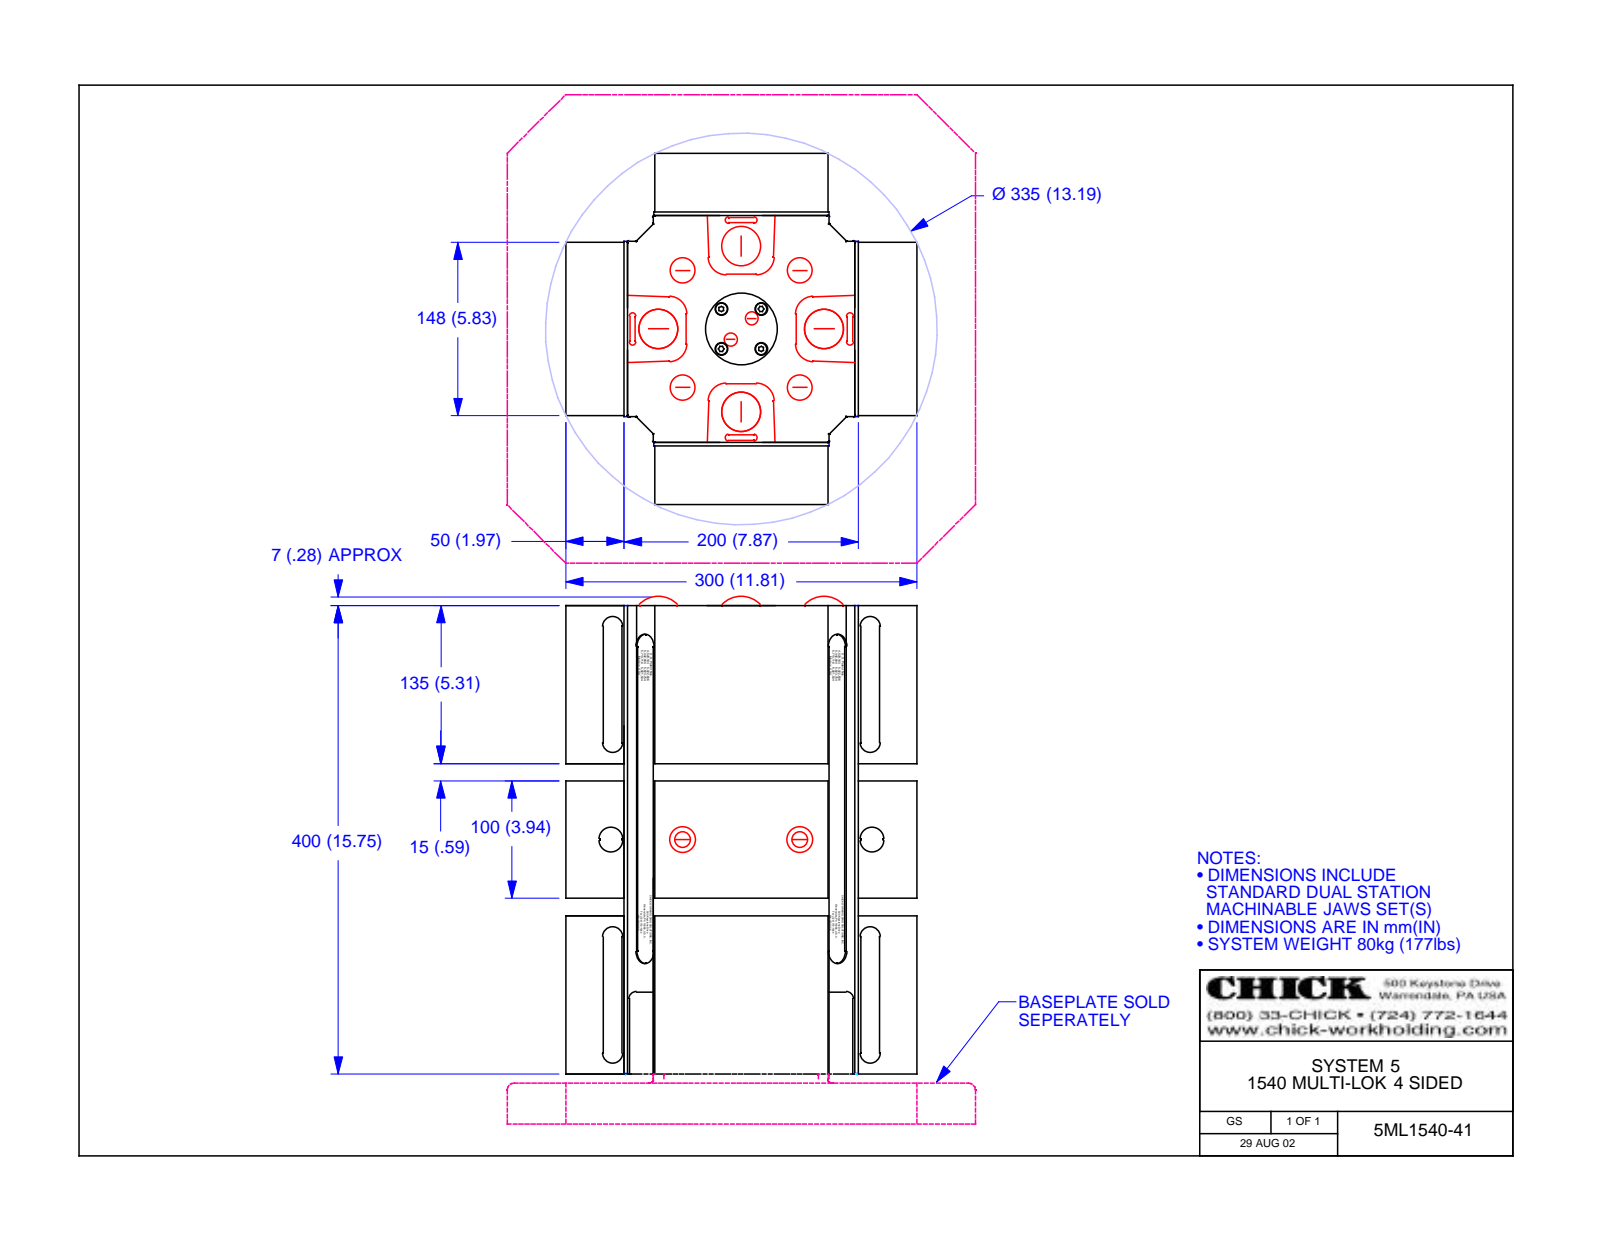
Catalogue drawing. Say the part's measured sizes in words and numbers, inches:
The part is named "5ML1540-41; 5CLM1540-41CM; 5CP1540-ST; 5DS1540-15-50 (+2 more)". Its 3-D file was written by "Autodesk Inventor 2013 (AUTOMOTIVE_DESIGN)". It is 17 solids with 2544 faces: 1308 planar, 456 cylindrical and 780 other. Overall it measures 16.031 by 11.811 by 11.811 inches. Its volume is 1 367 cubic inches and its surface area 2 866 square inches. Round holes: 12 of diameter 0.406, 12 of diameter 0.433, 12 of diameter 0.715, 12 of diameter 1.062, 8 of diameter 0.398, 8 of diameter 0.669, 8 of diameter 0.787, 6 of diameter 0.394, 4 of diameter 0.16, 4 of diameter 0.194, 4 of diameter 0.27, 4 of diameter 0.413. Round bosses or shafts: 8 of diameter 0.335, 4 of diameter 0.302, 4 of diameter 0.187. Partial cylindrical surfaces (rounded edges, fillets, slot ends): 88 of radius 0.079, 16 of radius 0.016, 16 of radius 0.047, 16 of radius 0.118, 16 of radius 0.626, 8 of radius 0.065, 8 of radius 0.111, 8 of radius 0.404. The main face-to-face distances are 0.118, 7.756, 9.843, 1.969, 7.874, 2.087, 9.724, 7.638, 6.732, 4.489. The hole center spacings are 3.937, 0.048, 1.181, 3.714, 4.11, 4.921, 5.118, 5.253.
